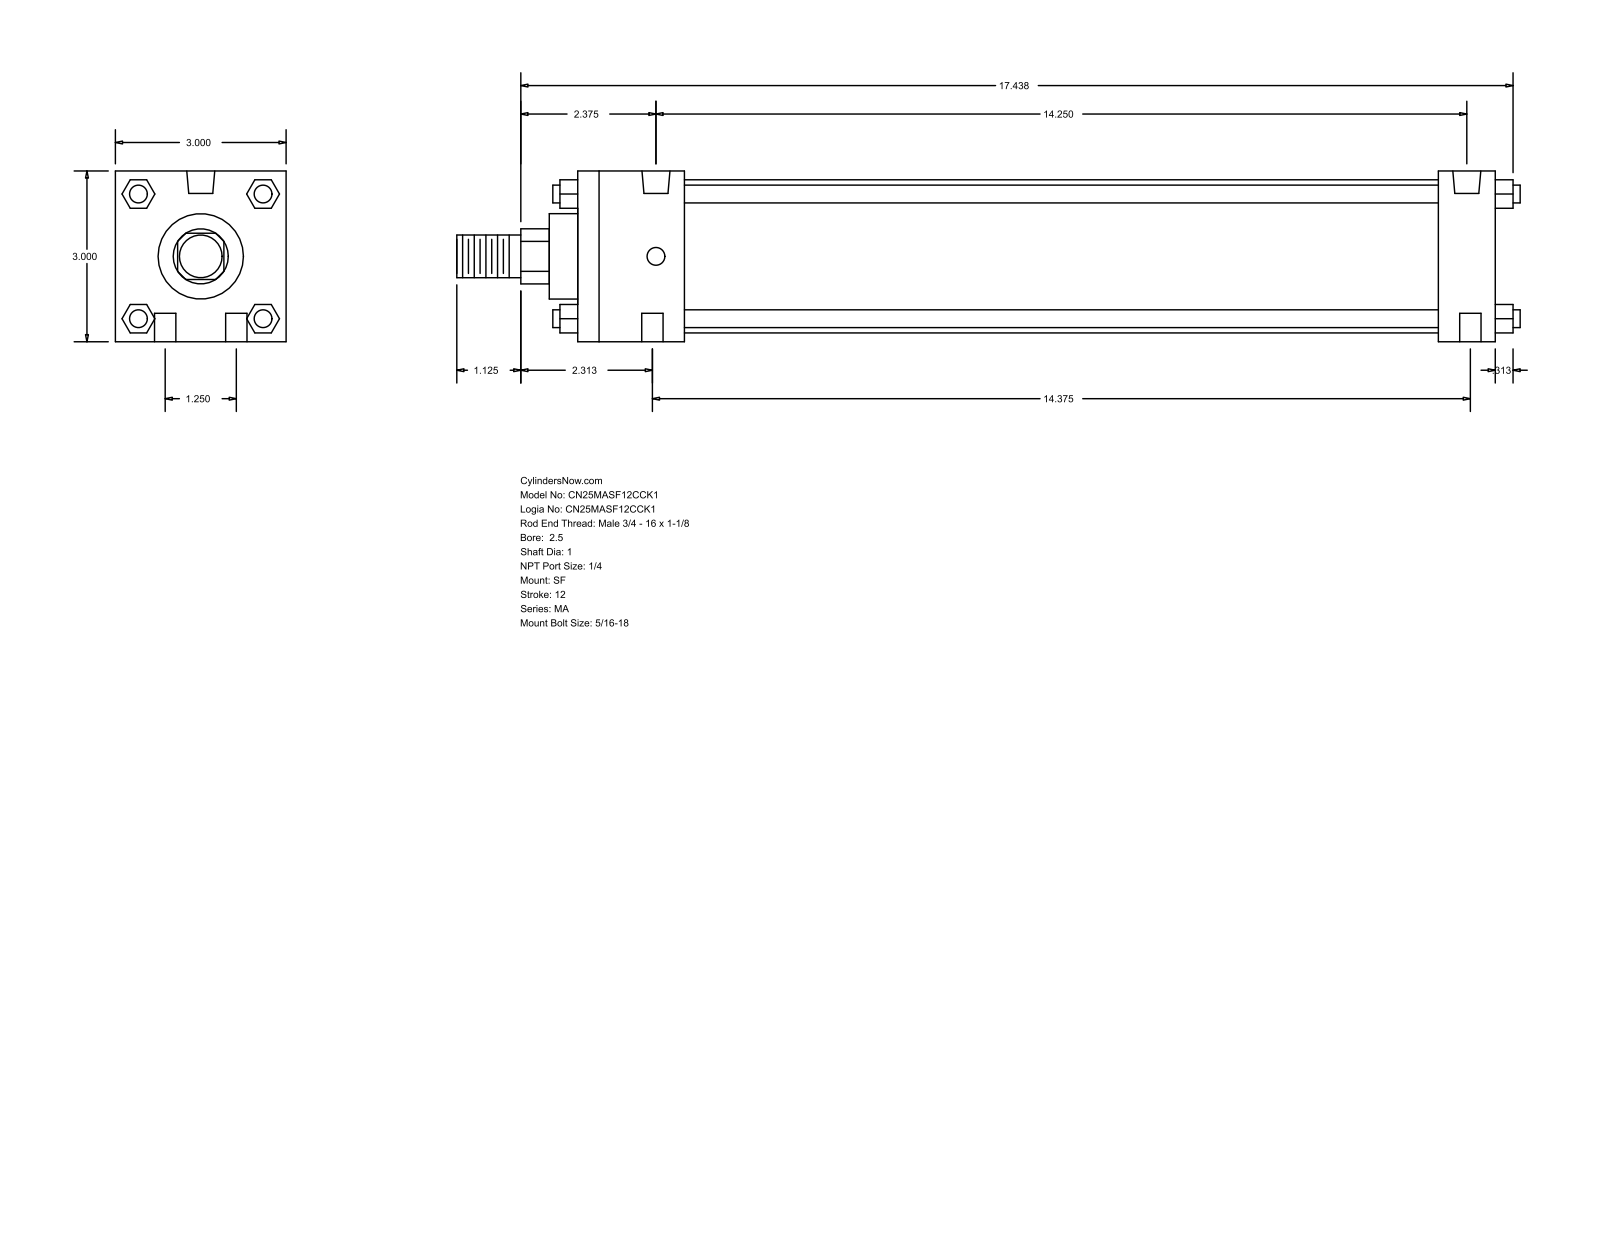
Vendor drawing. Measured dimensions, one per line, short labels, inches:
name: MA_SF__0250_1
written by: GSSL Pune (CONFIG_CONTROL_DESIGN)
unit: in
bodies: 0 solids, 124 faces (94 planar, 30 cylindrical, 0 other)
size: 18.687 × 3 × 3
holes: 4× ⌀0.375, 2× ⌀0.313, 2× ⌀0.492
bosses: 4× ⌀0.313, 1× ⌀2.69, 1× ⌀1.5, 1× ⌀1, 1× ⌀0.75
rounds: 1× R0.484
face distances: 3, 16.125, 0.5, 15.125, 1, 1.875, 13.25, 14.25, 1.095, 1.896
hole spacings: 0.628, 14.326, 1.25, 14.25, 14.375, 14.429
